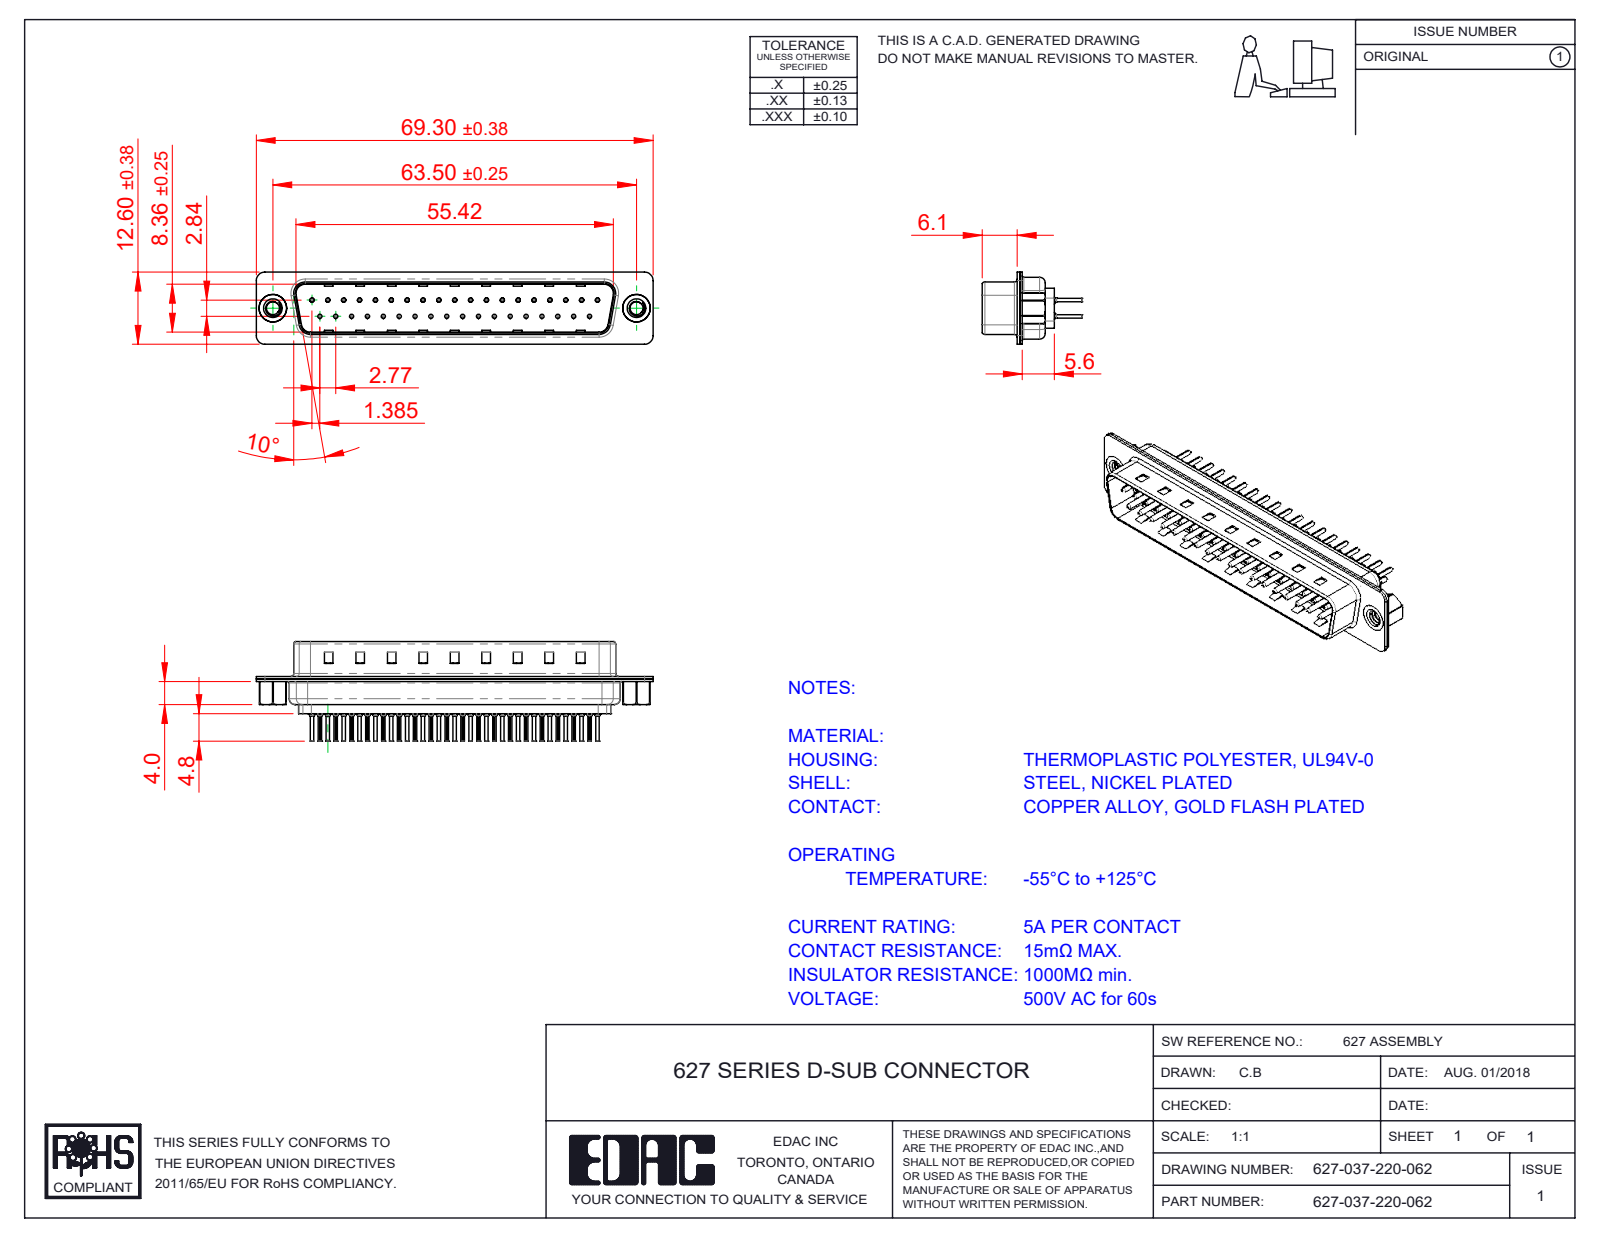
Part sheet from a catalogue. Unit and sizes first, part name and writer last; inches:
Units: inches
Overall size (bounding box): 2.728 × 0.681 × 0.496
Round holes (diameter × count): ⌀0.008 ×37, ⌀0.014 ×37, ⌀0.043 ×37, ⌀0.063 ×37, ⌀0.089 ×2, ⌀0.157 ×2, ⌀0.189 ×2
Round bosses / shafts (diameter × count): ⌀0.079 ×37, ⌀0.059 ×37, ⌀0.03 ×37, ⌀0.024 ×37, ⌀0.197 ×2, ⌀0.193 ×2
Partial cylindrical surfaces — rounded edges, fillets, slot ends (radius × count): R0.004 ×74, R0.059 ×16, R0.079 ×12, R0.02 ×8, R0.063 ×8, R0.01 ×4, R0.024 ×4, R0.026 ×4
Main face-to-face distances: 0.016, 0.032, 0.377, 0.018, 0.345, 0.059, 0.035, 0.055, 0.238, 0.017
Hole centre spacings: 0.124, 0.109, 0.218, 0.327, 0.198, 0.398, 0.436, 0.503
Volume: 0.226 in³ · Surface area: 16.54 in²
Bodies: 42 solids, 4034 faces (1091 planar, 1508 cylindrical, 1435 other)
Part name (STEP PRODUCT): 627 Housing_37 LP; 627 Contact Row 1_20L; 627 4-40 Threaded Rivet; 627-037-220-062 (+3 more)
STEP written by: SolidWorks 2020 (CONFIG_CONTROL_DESIGN)
